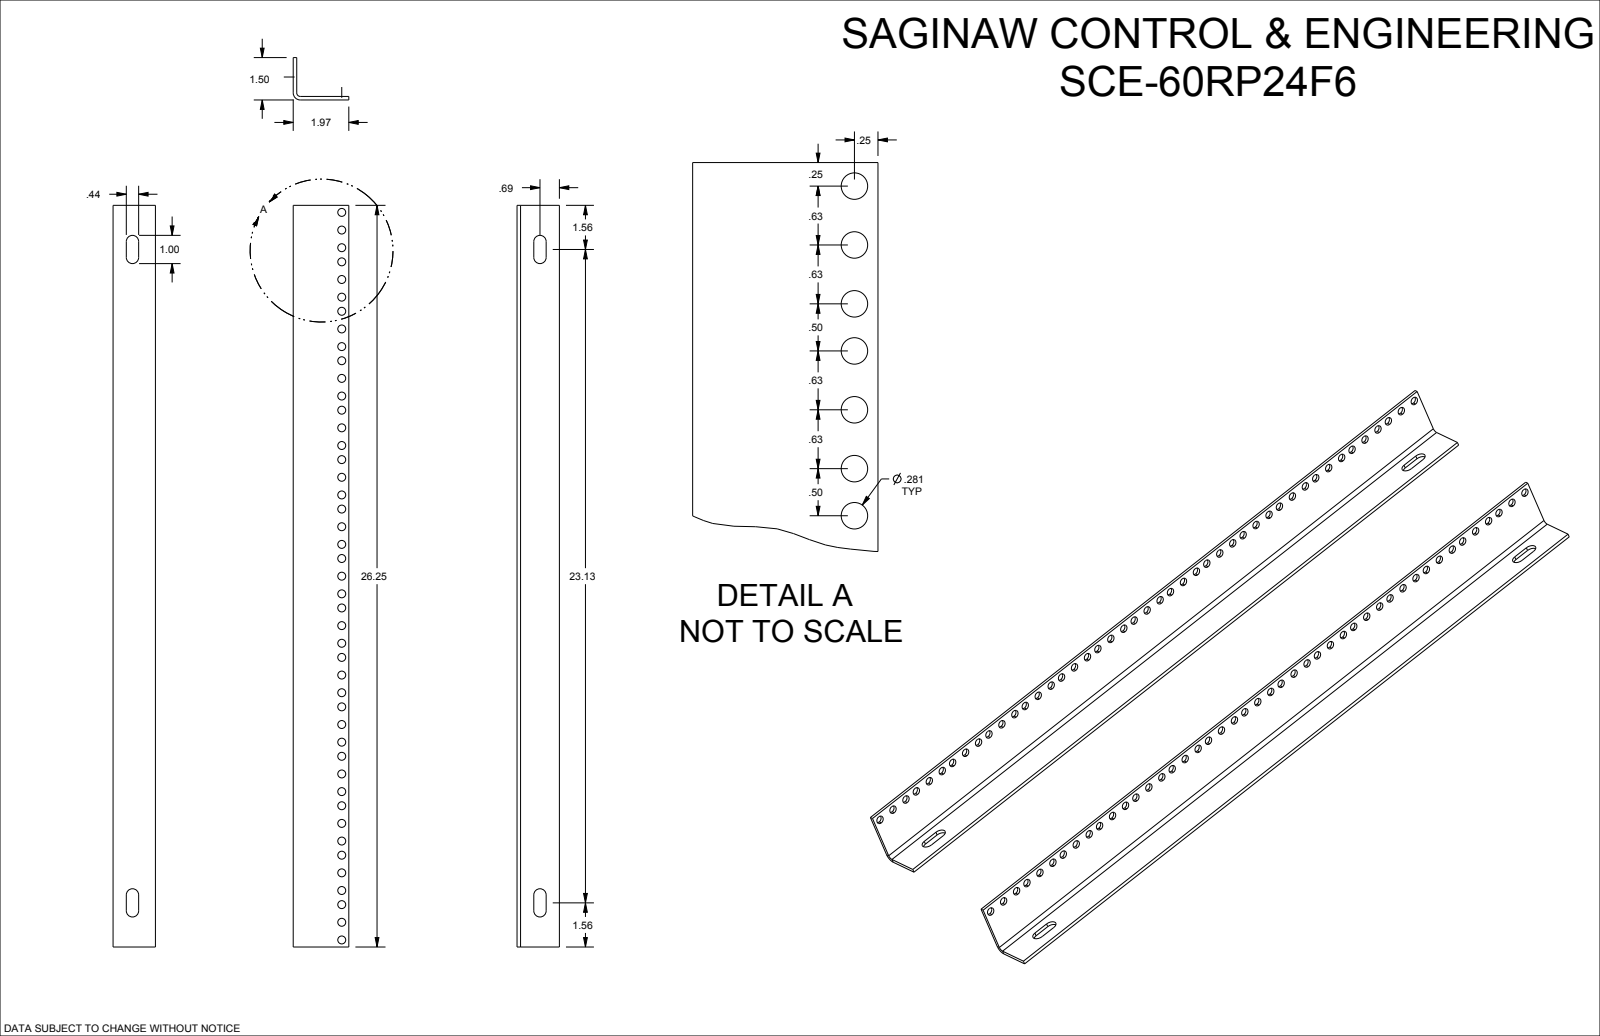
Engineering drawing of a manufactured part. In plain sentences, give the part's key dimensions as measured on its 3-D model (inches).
The part is named "SCE-60RP24F6". Its 3-D file was written by "SolidWorks 2019 (CONFIG_CONTROL_DESIGN)". It is 1 solid with 112 faces: 16 planar, 96 cylindrical and 0 other. Overall it measures 26.25 by 1.969 by 1.5 inches. Its volume is 10.26 cubic inches and its surface area 177.1 square inches. Round holes: 45 of diameter 0.281. Partial cylindrical surfaces (rounded edges, fillets, slot ends): 4 of radius 0.219, 1 of radius 0.125, 1 of radius 0.25. The main face-to-face distances are 0.125, 1.5, 1.375, 1.969, 1.844, 26.25, 0.594, 1.031, 0.469, 0.906. The hole center spacings are 1.75, 3.5, 5.25, 7, 8.75, 0.625, 0.625, 1.25.
